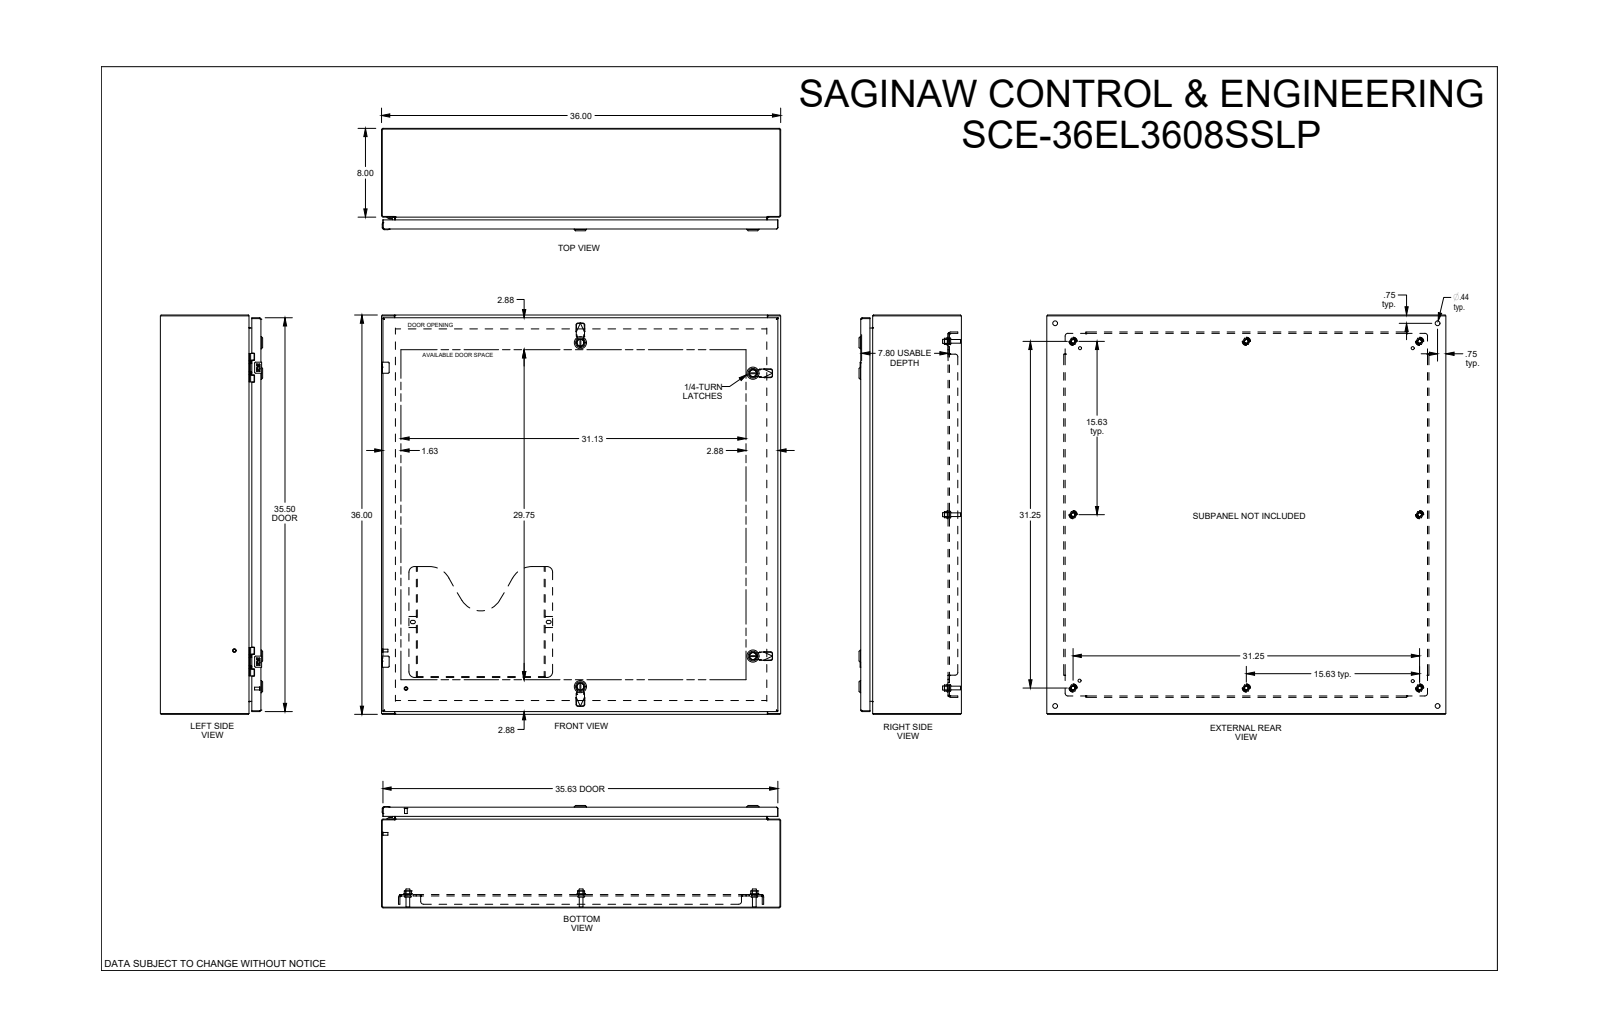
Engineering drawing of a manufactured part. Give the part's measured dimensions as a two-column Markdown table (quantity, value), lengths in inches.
| quantity | value |
| --- | --- |
| part name | SCE-36EL3608SSLP |
| STEP written by | SolidWorks 2019 (CONFIG_CONTROL_DESIGN) |
| units | inches |
| bodies | 0 solids, 3904 faces (1851 planar, 1049 cylindrical, 1004 other) |
| overall size | 36 × 36 × 9.23 |
| round holes (diameter × count) | 0.367 × 8, 0.5 × 8, 0.172 × 4, 0.197 × 4, 0.205 × 4, 0.244 × 4, 0.266 × 4, 0.281 × 4, 0.315 × 4, 0.375 × 4, 0.394 × 4, 0.437 × 4 |
| round bosses / shafts (diameter × count) | 0.366 × 8, 0.332 × 8, 0.17 × 6, 1.102 × 4, 0.866 × 4, 0.802 × 4, 0.78 × 4, 0.63 × 4 |
| partial cylindrical surfaces (radius × count) | 0.012 × 116, 0.01 × 52, 0.02 × 44, 0.015 × 28, 0.04 × 23, 0.157 × 16, 0.07 × 14, 0.029 × 12 |
| main face-to-face distances | 0.075, 0.075, 8.923, 8.998, 9.073, 8.998, 1.2, 7.873, 35.925, 1 |
| hole center spacings | 15.625, 17.326, 26.5, 32.915, 34.939, 37.126, 0.985, 15.019 |
